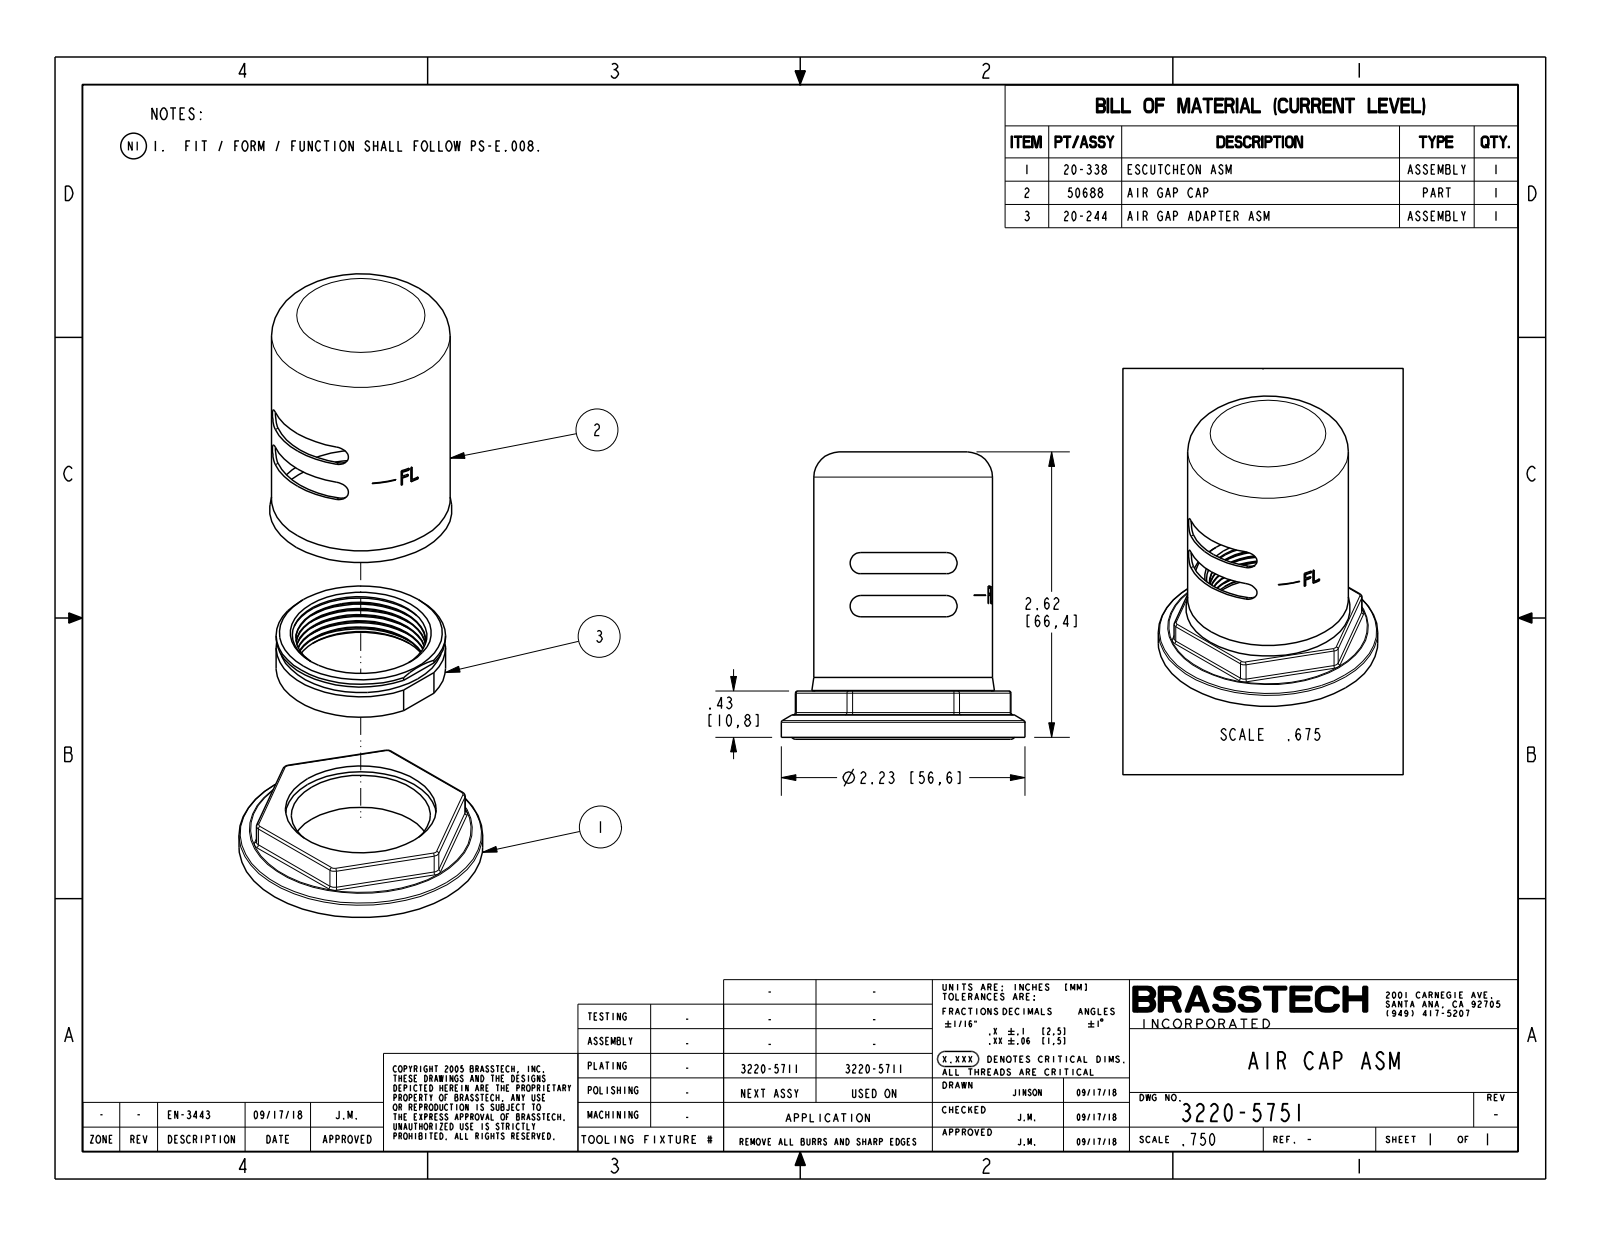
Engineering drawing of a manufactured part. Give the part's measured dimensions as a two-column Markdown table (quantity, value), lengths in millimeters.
| quantity | value |
| --- | --- |
| part name | 12924; 20-338_ASM; 50688; 12736 (+3 more) |
| STEP written by | PRO/ENGINEER BY PARAMETRIC TECHNOLOGY CORPORATION, 2013150 (CONFIG_CONTROL_DESIGN) |
| units | millimeters |
| bodies | 4 solids, 202 faces (56 planar, 80 cylindrical, 66 other) |
| overall size | 66.4 × 56.6 × 56.6 |
| volume | 22 500 mm³ |
| surface area | 41 810 mm² |
| round holes (diameter × count) | 30.2 × 1, 32.3 × 1, 35.1 × 1, 40 × 1, 53.7 × 1 |
| round bosses / shafts (diameter × count) | 56.6 × 1, 47.6 × 1, 41.5 × 1, 39.4 × 1, 35.3 × 1, 34.5 × 1 |
| partial cylindrical surfaces (radius × count) | 0.5 × 12, 1.5 × 6, 2.5 × 4, 20.5 × 1 |
| main face-to-face distances | 55.6, 10.8, 66.4, 65.7, 54.9, 0.8, 5.3, 5.5, 60.4, 61.2 |
